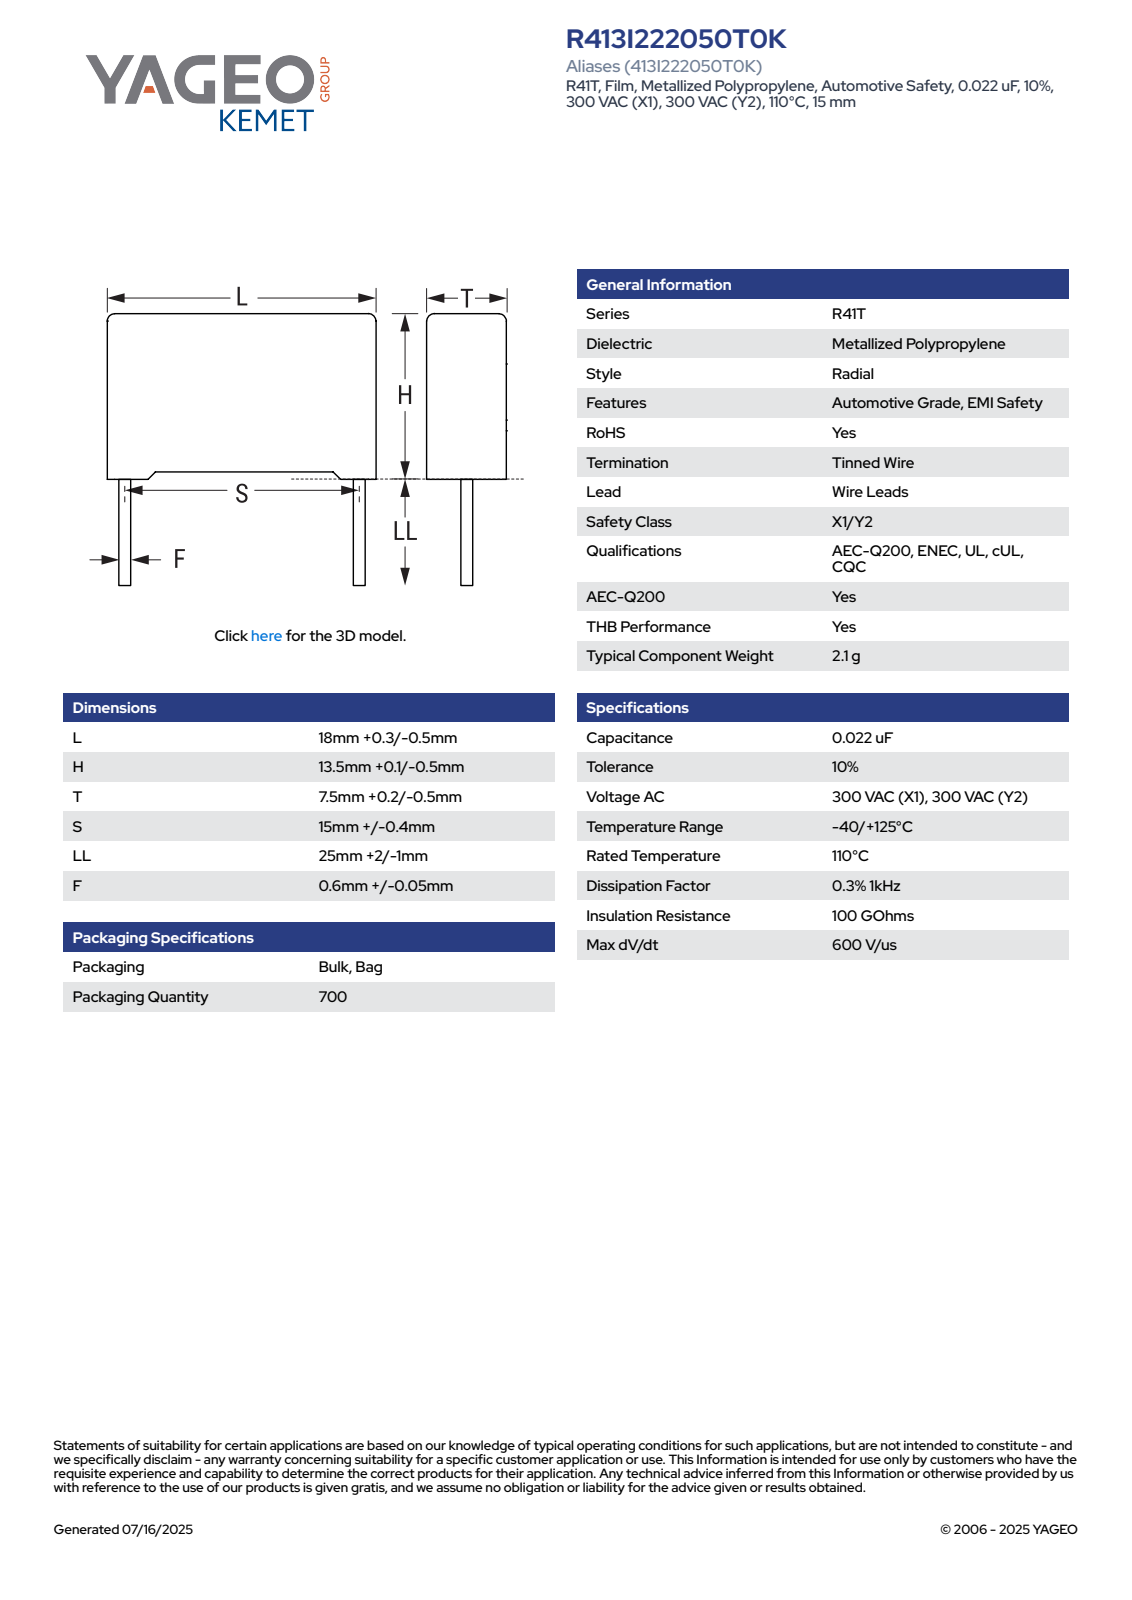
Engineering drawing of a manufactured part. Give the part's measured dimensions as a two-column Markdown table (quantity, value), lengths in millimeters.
| quantity | value |
| --- | --- |
| part name | CFR_RB2_18X13.5X7.5_L18.3H13.6T7.7S15LL27F0.65 |
| STEP written by | SolidWorks 2021 (AUTOMOTIVE_DESIGN) |
| units | millimeters |
| bodies | 4 solids, 85 faces (77 planar, 8 cylindrical, 0 other) |
| overall size | 40.6 × 18.3 × 7.71 |
| volume | 1 843 mm³ |
| surface area | 1 131 mm² |
| round bosses / shafts (diameter × count) | 0.65 × 2 |
| partial cylindrical surfaces (radius × count) | 0.5 × 4 |
| main face-to-face distances | 7.7, 12.85, 18.3, 0.61, 0.75, 13.6, 7.09, 0.47, 13.13, 17.69 |
